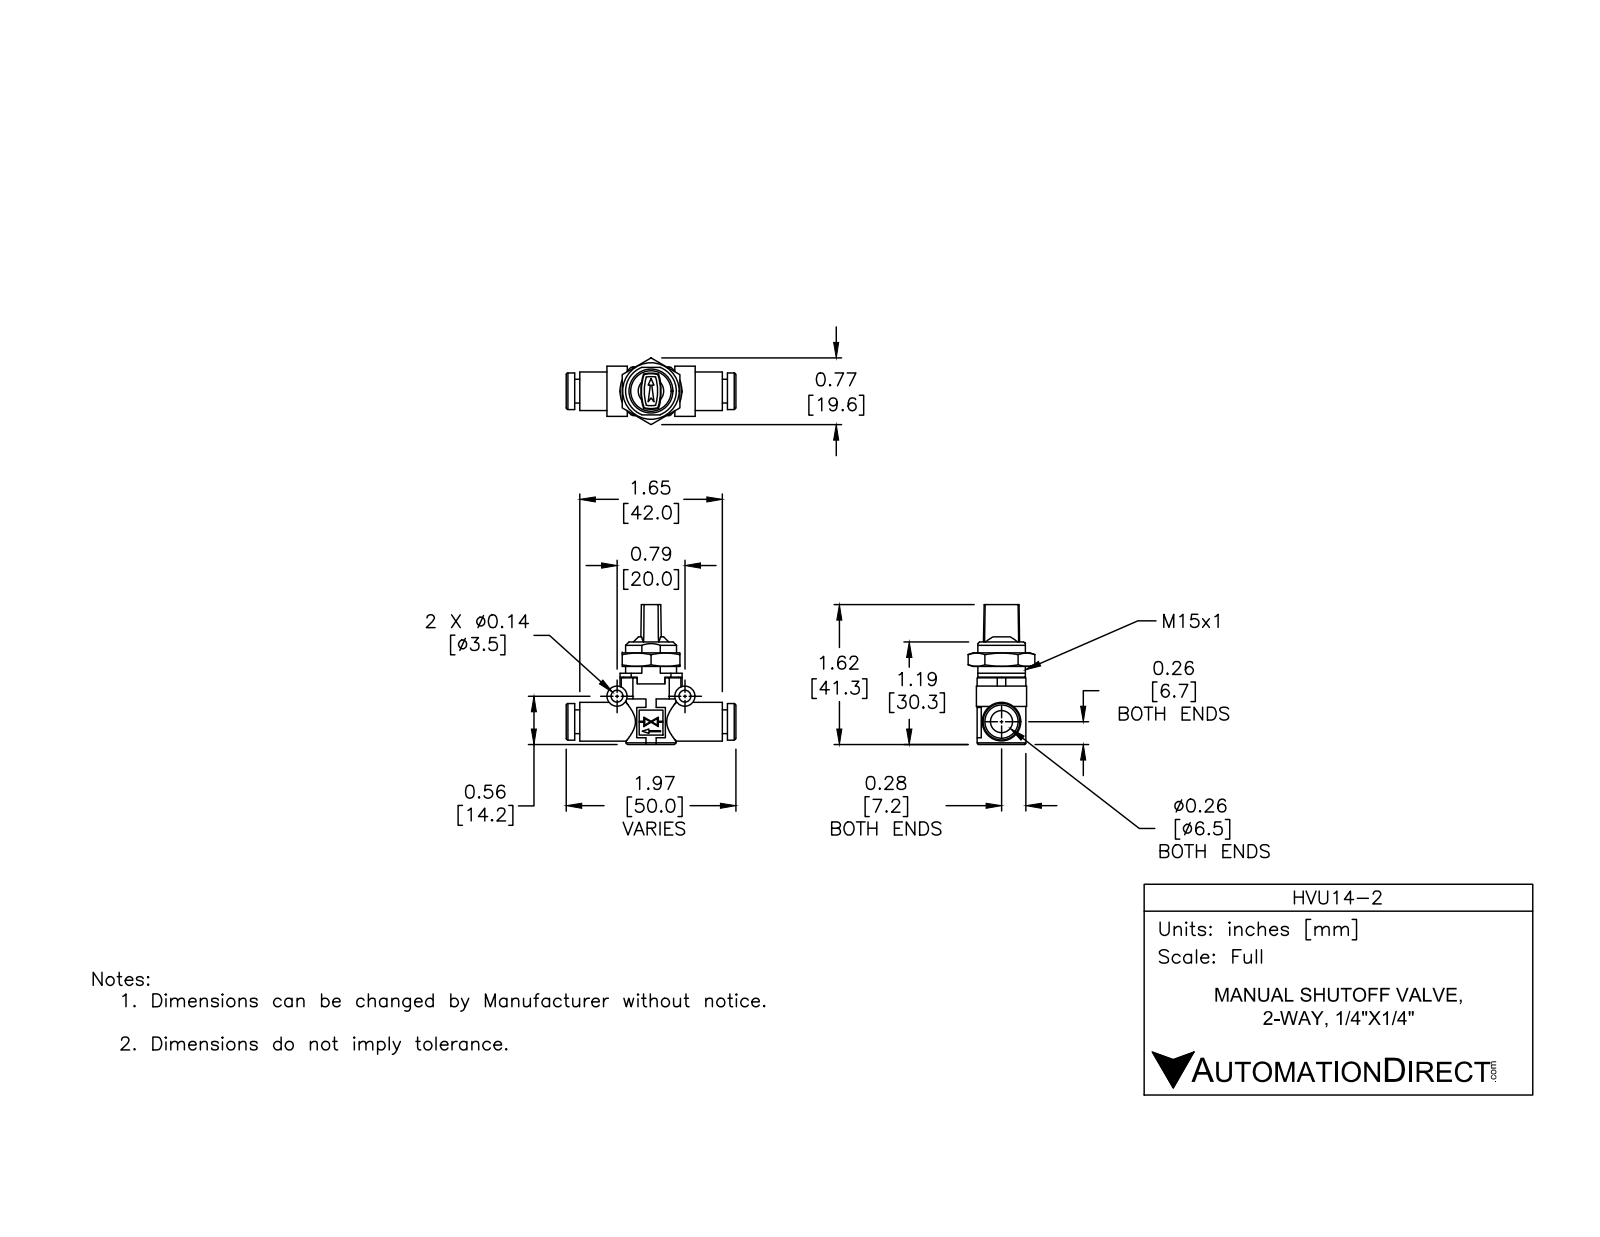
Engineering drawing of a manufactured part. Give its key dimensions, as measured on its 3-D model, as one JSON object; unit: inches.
{"part_name": "HVU14-2", "step_written_by": "SolidWorks 2015 (CONFIG_CONTROL_DESIGN)", "units": "inches", "bodies": {"solids": 4, "faces": 179, "planar": 110, "cylindrical": 49, "other": 20}, "overall_size": [1.969, 1.624, 0.773], "volume_in3": 0.543, "surface_area_in2": 10.4, "round_holes": [[0.138, 2], [0.256, 1], [0.295, 1], [0.472, 1]], "round_bosses_or_shafts": [[0.236, 2], [0.577, 1], [0.449, 1], [0.425, 1], [0.276, 1]], "partial_cylinders_radius": [[0.02, 2], [0.098, 2], [0.277, 2], [0.573, 2], [0.295, 1], [0.359, 1]], "face_to_face_distances": [0.551, 0.703, 0.65, 0.157, 0.059, 0.558, 0.079, 1.713, 0.669, 0.124], "hole_center_spacings": [0.787]}
